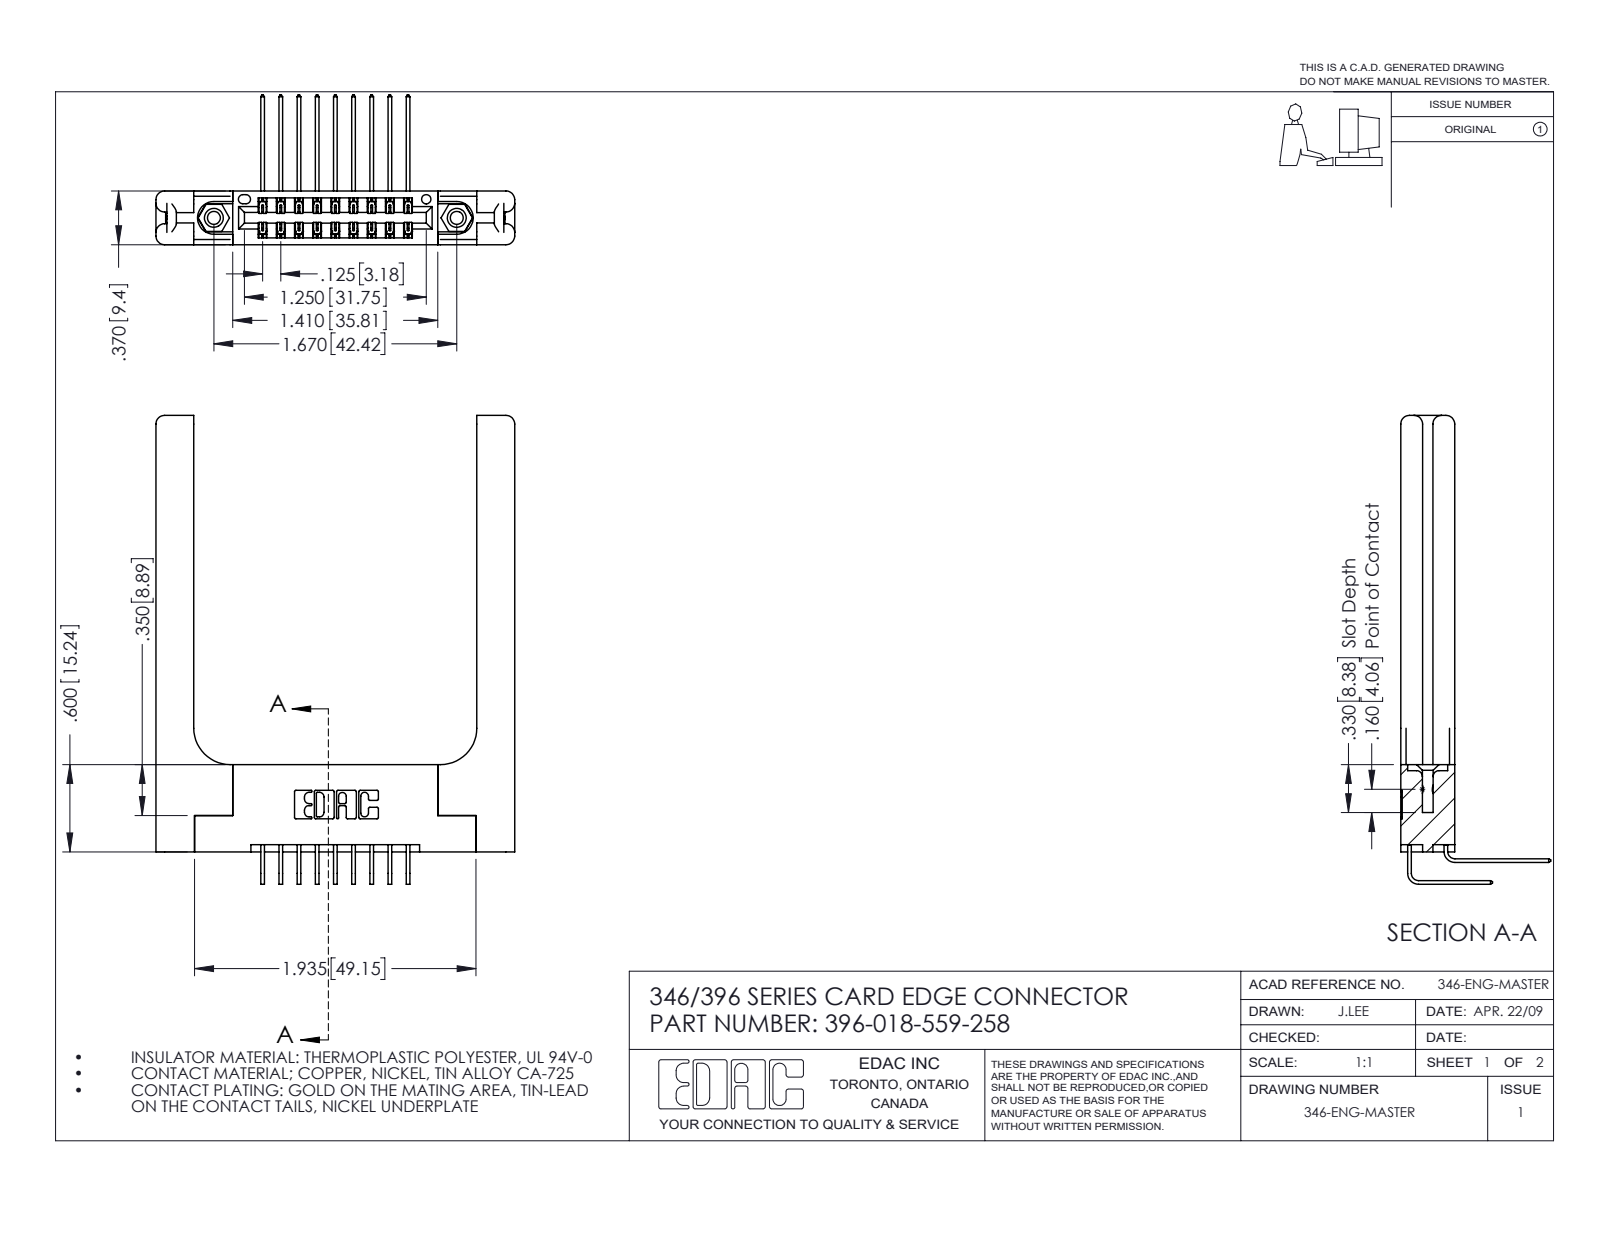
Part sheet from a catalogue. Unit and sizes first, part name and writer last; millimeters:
Units: millimetres
Overall size (bounding box): 81.9 × 62.6 × 26.2
Round holes (diameter × count): ⌀2.3 ×2, ⌀3.2 ×2, ⌀4 ×2, ⌀1.6 ×1
Round bosses / shafts (diameter × count): ⌀3.9 ×2
Partial cylindrical surfaces — rounded edges, fillets, slot ends (radius × count): R0.2 ×27, R0.3 ×22, R1.5 ×16, R0.2 ×6, R0.8 ×6, R0.7 ×3, R0.4 ×2, R0.6 ×2
Main face-to-face distances: 9.4, 3.8, 1.8, 5.6, 1.2, 8.2, 3.8, 6.4, 2.6, 4.4
Hole centre spacings: 6.2, 37.2, 42.4
Volume: 13 500 mm³ · Surface area: 13 140 mm²
Bodies: 23 solids, 1350 faces (890 planar, 400 cylindrical, 60 other)
Part name (STEP PRODUCT): 346-220-058_345-220-058; 345-250-001_345-250-001-102; 345-292-001_559 Tail - 2; 396-018-559-258 (+2 more)
STEP written by: SolidWorks 2016 (CONFIG_CONTROL_DESIGN)
